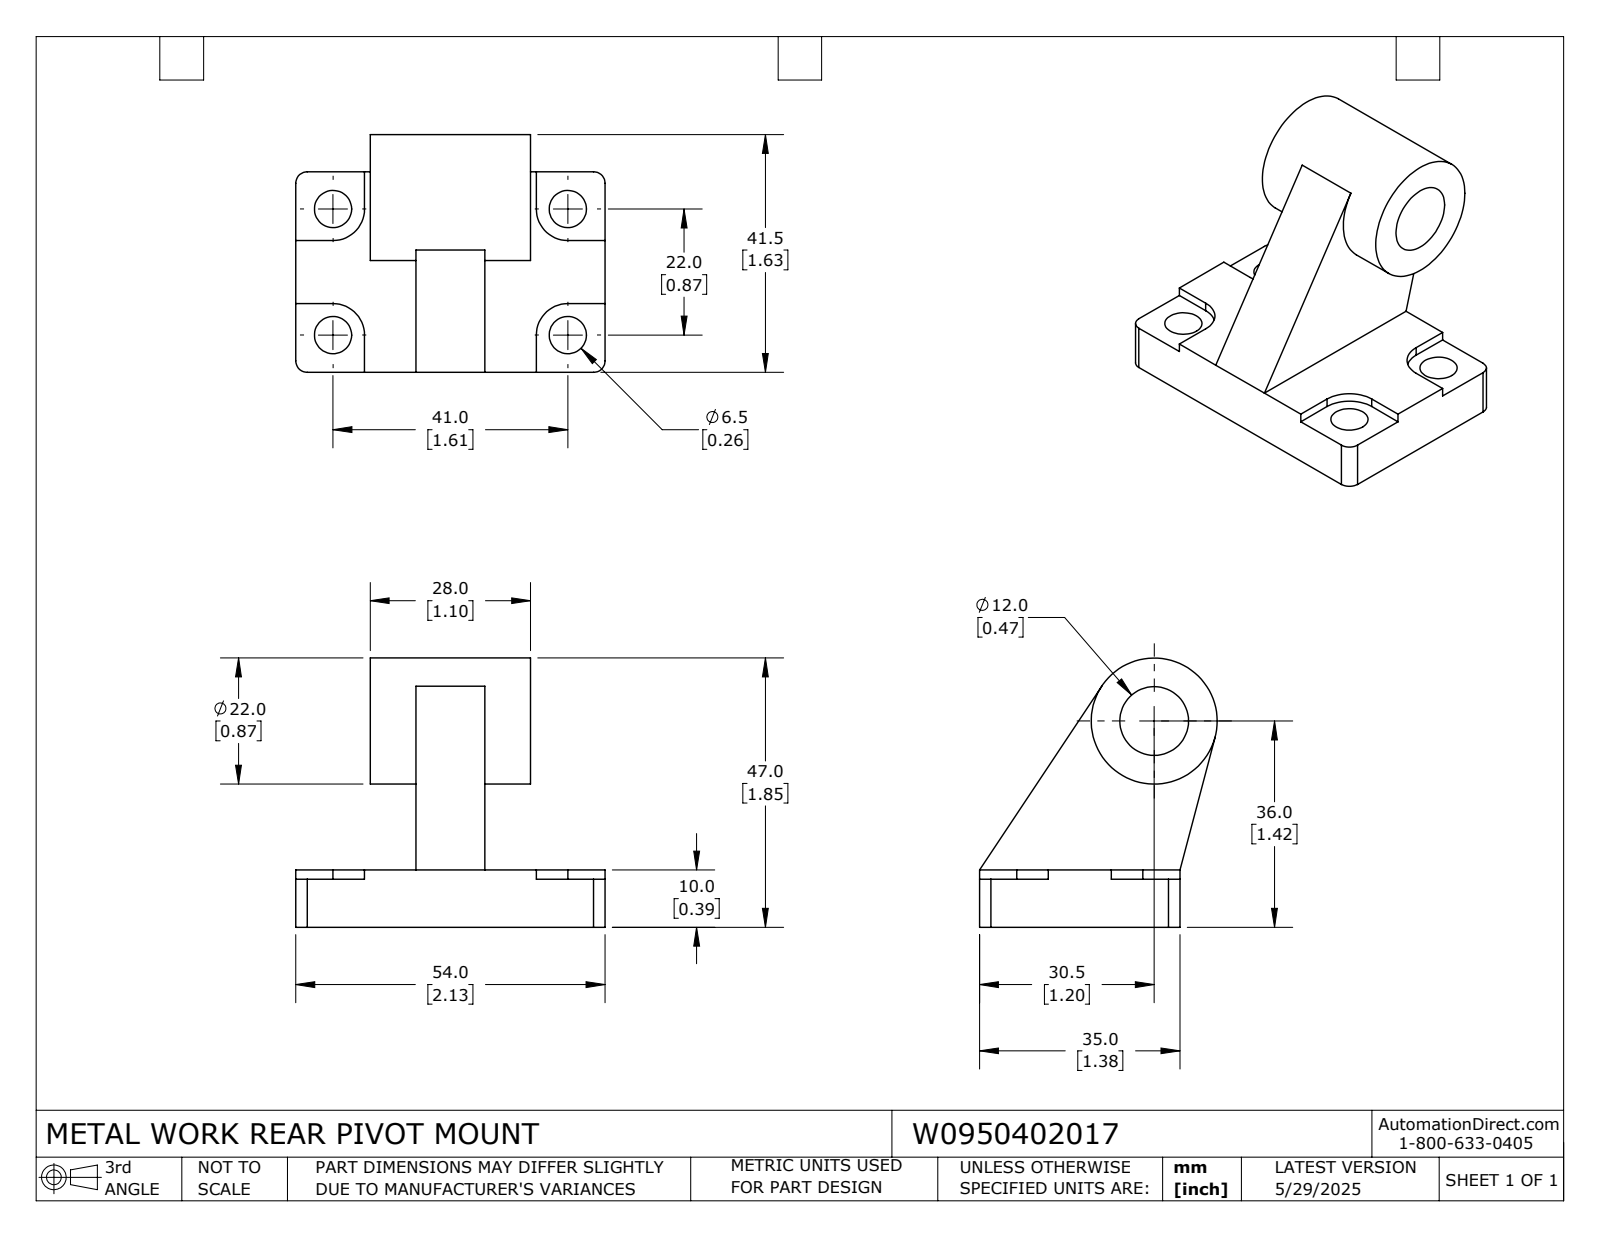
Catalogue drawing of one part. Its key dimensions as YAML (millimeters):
part_name: "W0950402017"
step_written_by: "SolidWorks 2024 (CONFIG_CONTROL_DESIGN)"
units: millimeters
bodies: {solids: 1, faces: 50, planar: 30, cylindrical: 20, other: 0}
overall_size: [54, 47, 41.5]
volume: 30098
surface_area: 10757
round_holes:
  - {diameter: 6.5, count: 4}
  - {diameter: 12, count: 1}
round_bosses_or_shafts:
  - {diameter: 22, count: 1}
partial_cylinders:
  - {radius: 2, count: 4}
  - {radius: 5.5, count: 4}
face_to_face_distances: [10, 21, 12, 7, 33, 13, 41, 8, 20, 35]
hole_center_spacings: [22, 41, 46.53]
